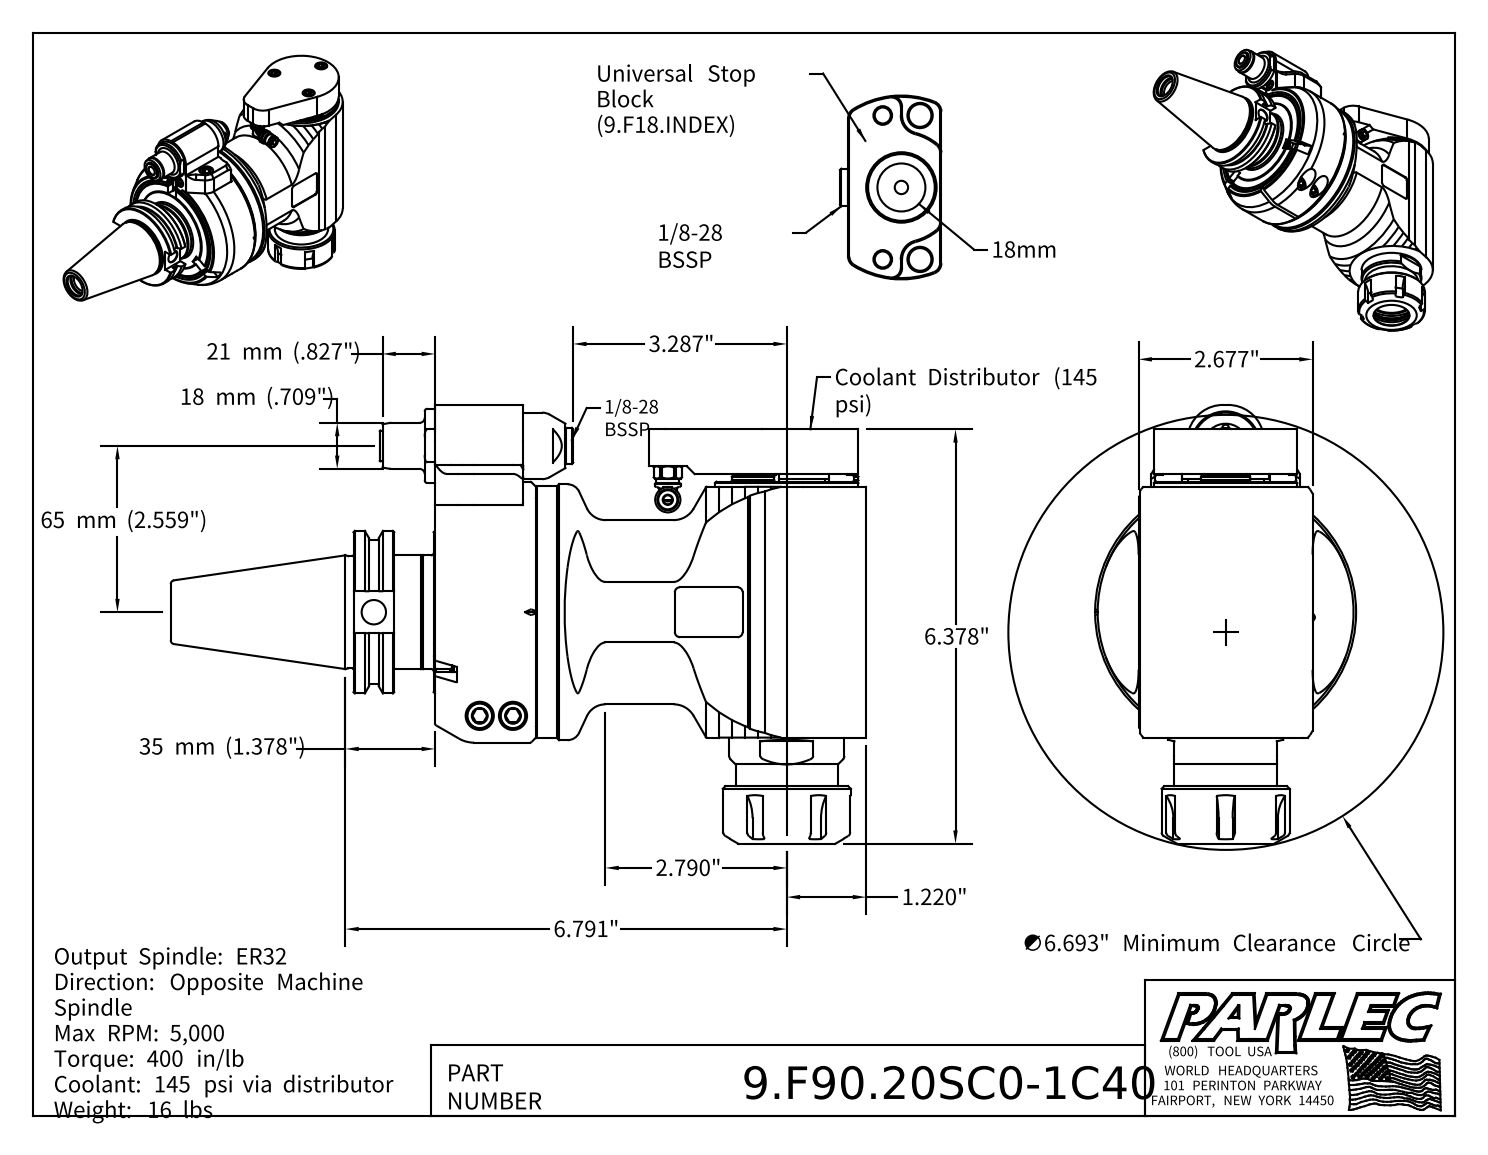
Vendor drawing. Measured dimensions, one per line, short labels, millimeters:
name: 9.F90.20SC0-1C40; F90-20SC; 9_GA1_446_2 (EVO, Type 1, C40, 65mm, 35mm)
written by: Autodesk Inventor 2022 (AUTOMOTIVE_DESIGN)
unit: mm
bodies: 4 solids, 865 faces (363 planar, 223 cylindrical, 279 other)
size: 271.8 × 171.5 × 102
volume: 1 251 000 mm³; area: 170 300 mm²
holes: 7× ⌀3.2, 3× ⌀5, 3× ⌀5.5, 3× ⌀6.5, 3× ⌀9, 3× ⌀12.5, 2× ⌀2.6, 2× ⌀3.3, 2× ⌀3.5, 2× ⌀4.2, 2× ⌀8, 2× ⌀10.4
bosses: 5× ⌀10, 3× ⌀12, 3× ⌀8.5, 3× ⌀5, 2× ⌀40, 2× ⌀18, 2× ⌀14, 2× ⌀6
rounds: 18× R1, 13× R2, 6× R3, 6× R15, 4× R0.5, 4× R4, 3× R0.2, 2× R3.5
face distances: 0.5, 1, 7, 32, 8.5, 7.5, 3, 6.5, 32.5, 14
hole spacings: 8.3, 11.7, 21, 23.6, 46.5, 25.5, 7, 12.8
